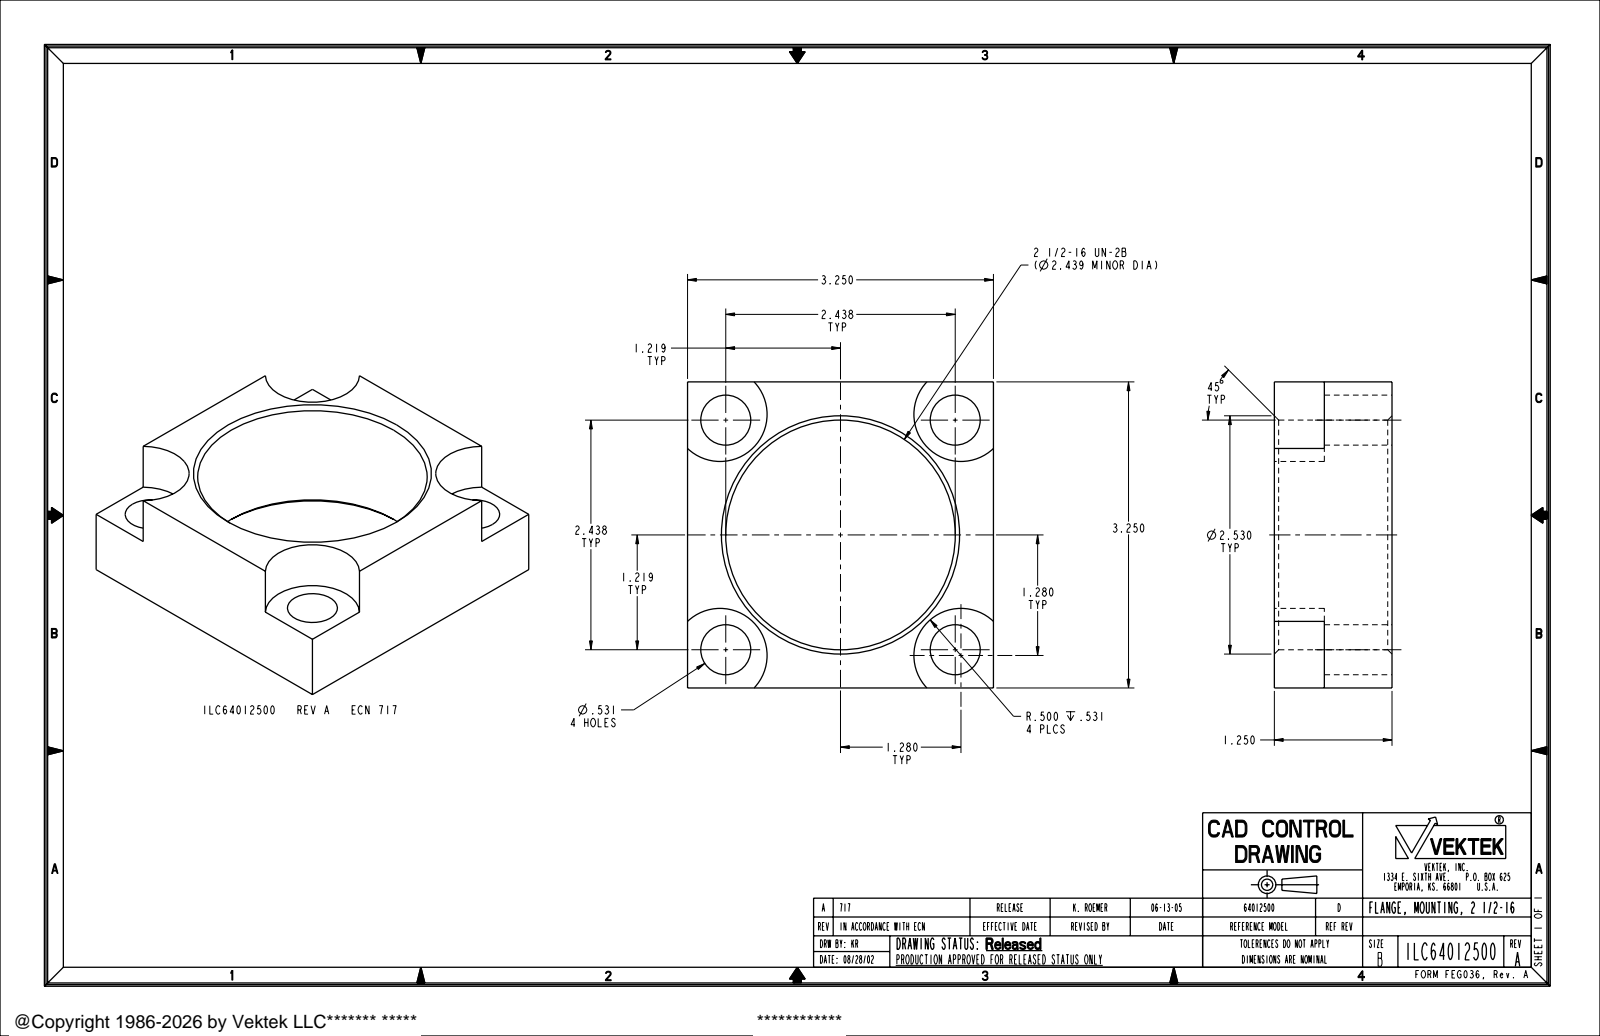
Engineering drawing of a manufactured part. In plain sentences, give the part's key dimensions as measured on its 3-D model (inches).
The part is named "ILC64012500". Its 3-D file was written by "PRO/ENGINEER BY PARAMETRIC TECHNOLOGY CORPORATION, 2004290 (AUTOMOTIVE_DESIGN_CC2)". It is 1 solid with 28 faces: 10 planar, 14 cylindrical and 4 other. Overall it measures 3.25 by 3.25 by 1.25 inches. Its volume is 5.371 cubic inches and its surface area 40.51 square inches. Round holes: 4 of diameter 0.531, 1 of diameter 2.439. Partial cylindrical surfaces (rounded edges, fillets, slot ends): 4 of radius 0.5. The main face-to-face distances are 3.25, 1.25, 0.719, 0.531. The hole center spacings are 1.724, 2.438, 3.448.
